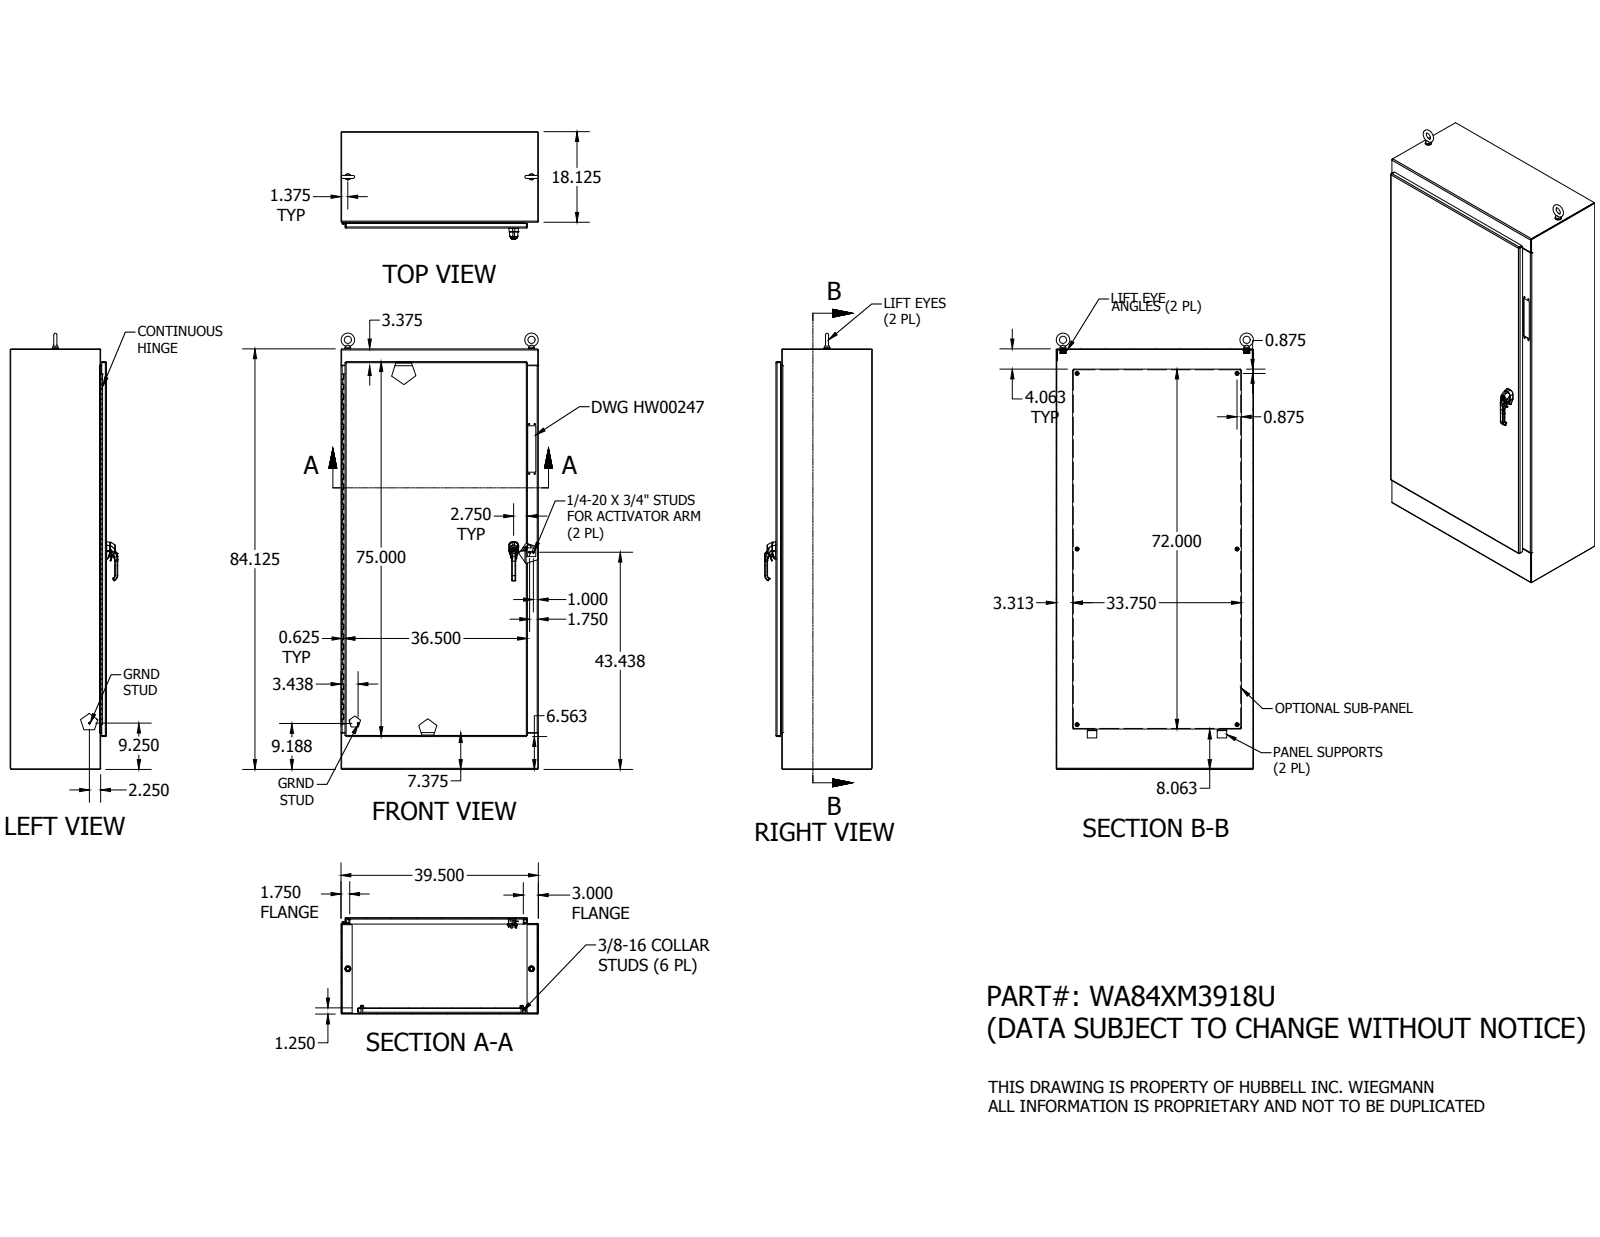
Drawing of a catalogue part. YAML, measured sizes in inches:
part_name: "WA84XM39U_BACK; WA84XM18U_RIGHT_SIDE; WA84XM18U_LEFT_SIDE; WAXM3918U_TOP_ENDWALL (+8 more)"
step_written_by: "Autodesk Inventor 2014 (AUTOMOTIVE_DESIGN)"
units: inches
bodies: {solids: 103, faces: 3776, planar: 1669, cylindrical: 1256, other: 851}
overall_size: [87.248, 39.5, 21.541]
volume: 1831
surface_area: 29790
round_holes:
  - {diameter: 0.375, count: 10}
  - {diameter: 0.276, count: 8}
  - {diameter: 0.281, count: 7}
  - {diameter: 0.156, count: 6}
  - {diameter: 0.25, count: 6}
  - {diameter: 0.307, count: 6}
  - {diameter: 0.563, count: 6}
  - {diameter: 0.2, count: 4}
  - {diameter: 0.29, count: 4}
  - {diameter: 0.213, count: 3}
  - {diameter: 0.118, count: 2}
  - {diameter: 0.125, count: 2}
round_bosses_or_shafts:
  - {diameter: 0.625, count: 10}
  - {diameter: 0.33, count: 9}
  - {diameter: 0.563, count: 6}
  - {diameter: 0.337, count: 4}
  - {diameter: 0.25, count: 4}
  - {diameter: 0.236, count: 3}
  - {diameter: 1.25, count: 2}
  - {diameter: 1.12, count: 2}
partial_cylinders:
  - {radius: 0.02, count: 187}
  - {radius: 0.012, count: 109}
  - {radius: 0.02, count: 48}
  - {radius: 0.019, count: 21}
  - {radius: 0.094, count: 21}
  - {radius: 0.219, count: 20}
  - {radius: 0.05, count: 14}
  - {radius: 0.079, count: 14}
face_to_face_distances: [0.125, 0.125, 1.125, 19.167, 19.042, 19.292, 19.167, 1.25, 17.917, 18.042]
hole_center_spacings: [30.388, 32, 35.125, 47.111, 0.38, 0.382, 0.382, 0.762]
